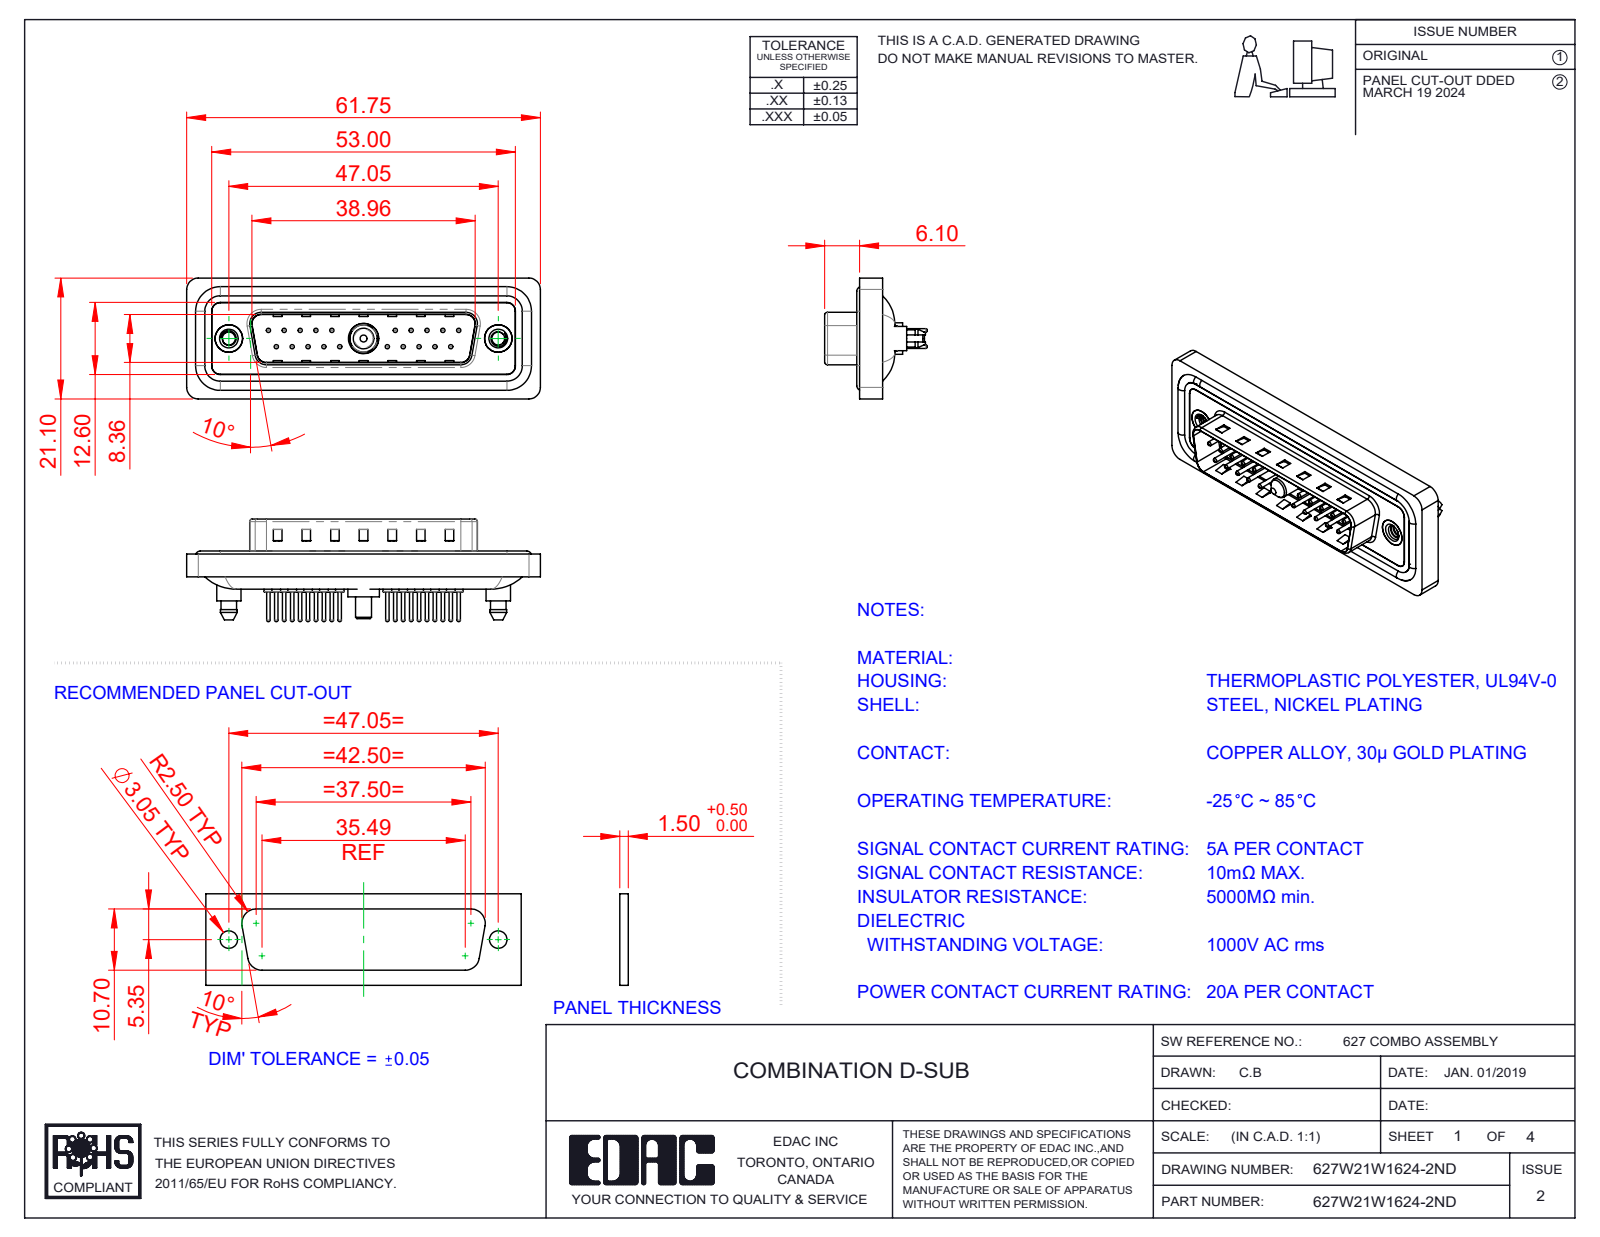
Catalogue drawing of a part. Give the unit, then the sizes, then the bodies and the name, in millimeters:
Units: millimetres
Overall size (bounding box): 61.75 × 21.1 × 17.9
Round holes (diameter × count): ⌀0.75 ×20, ⌀1.6 ×20, ⌀2 ×20, ⌀2.26 ×2, ⌀4 ×2, ⌀4.8 ×2, ⌀5 ×2, ⌀4.85 ×1, ⌀5.3 ×1
Round bosses / shafts (diameter × count): ⌀1.5 ×20, ⌀0.6 ×20, ⌀1.6 ×4, ⌀5.4 ×2, ⌀4.9 ×2, ⌀4.25 ×2, ⌀5.5 ×1, ⌀5.2 ×1
Partial cylindrical surfaces — rounded edges, fillets, slot ends (radius × count): R1.5 ×24, R2 ×18, R1.6 ×10, R0.5 ×8, R0.25 ×4, R0.6 ×4, R0.65 ×4, R0.9 ×4
Main face-to-face distances: 0.4, 1.5, 1.1, 1.6, 0.5, 3.1, 2.9, 4.1, 0.82, 9.58
Hole centre spacings: 3.16, 2.77, 5.54, 8.31, 5.04, 19.39, 20.97, 22.16
Volume: 7 332 mm³ · Surface area: 12 289 mm²
Bodies: 29 solids, 1320 faces (375 planar, 527 cylindrical, 418 other)
Part name (STEP PRODUCT): 627Combo Shell Rear_25 Contacts; 627Combo Shell Front_25 Contacts; 627Combo Waterproof Housing_25 Contacts; 627Combo Contact Row 2_24 (+6 more)
STEP written by: SolidWorks 2023 (CONFIG_CONTROL_DESIGN)
